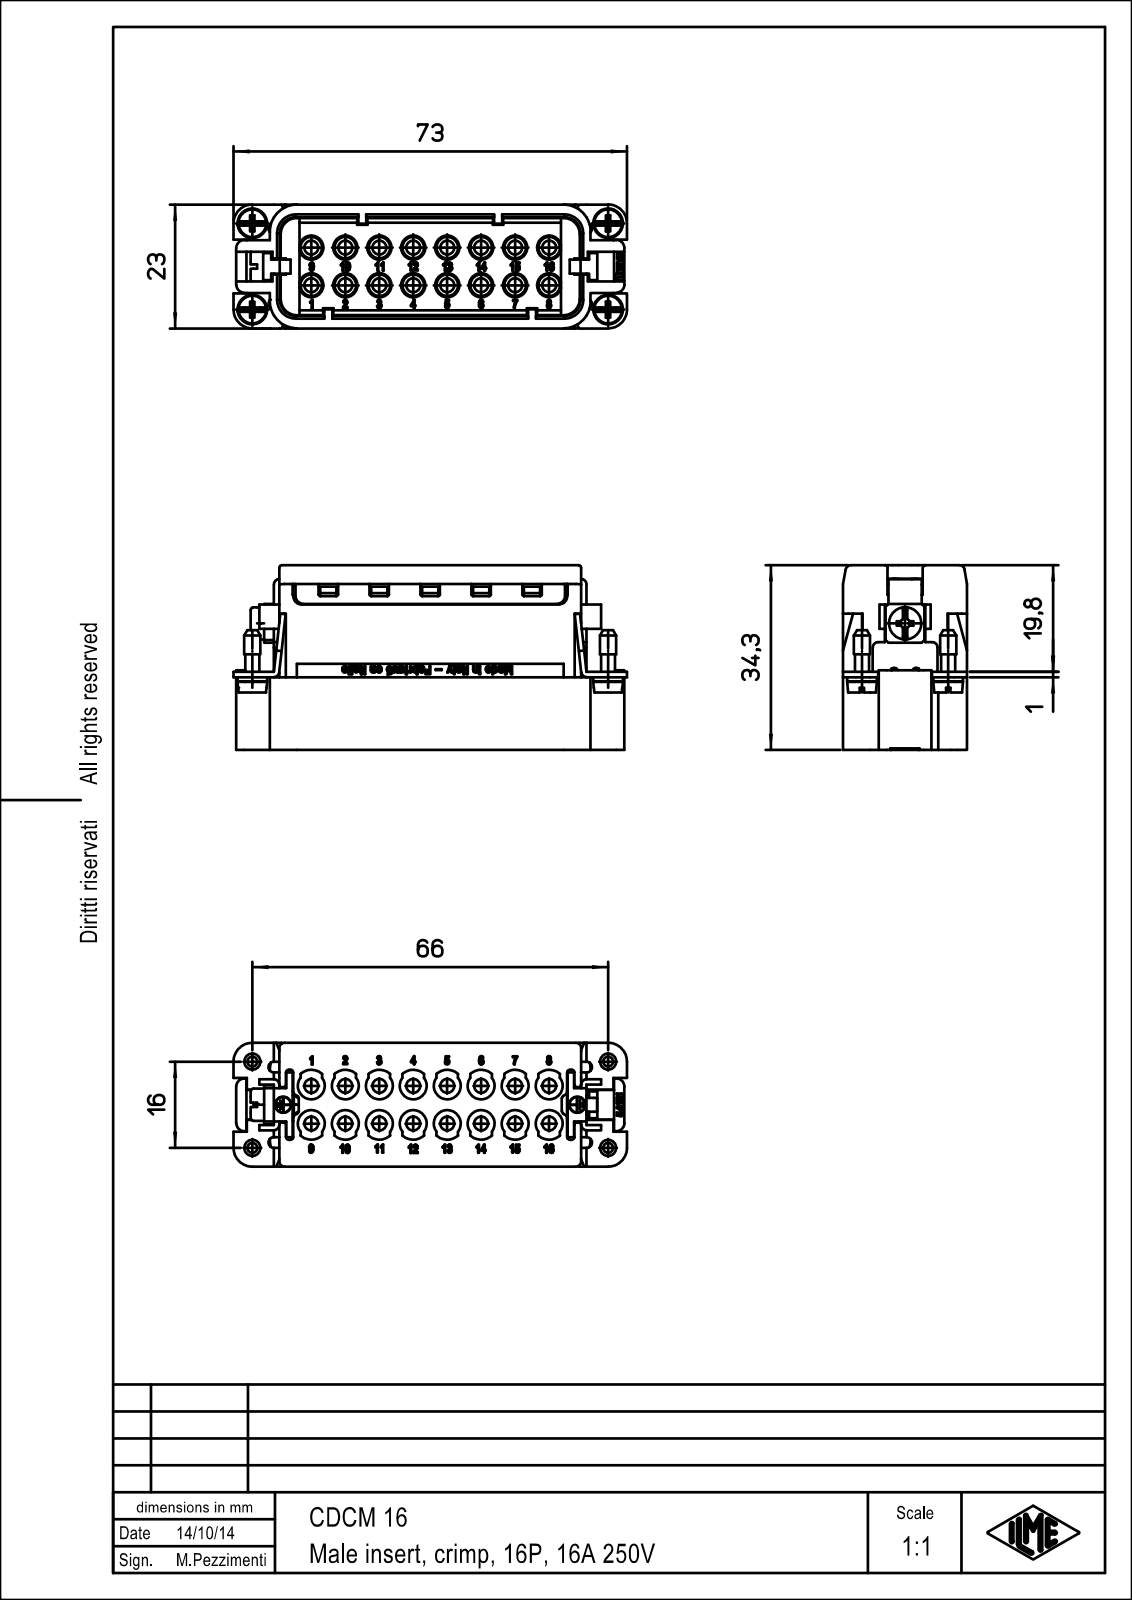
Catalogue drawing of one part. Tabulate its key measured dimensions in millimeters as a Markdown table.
| quantity | value |
| --- | --- |
| part name | CDCM_16 |
| STEP written by | PTC Creo Elements/Direct Modeling 19.0E 27-Jun-2016 (C) Parametric Technology GmbH (AUTOMOTIVE_DESIGN) |
| units | millimeters |
| bodies | 1 solid, 1579 faces (1144 planar, 301 cylindrical, 134 other) |
| overall size | 73 × 34.3 × 23 |
| volume | 41 736 mm³ |
| surface area | 18 809 mm² |
| round holes (diameter × count) | 4.6 × 16, 5 × 16, 2.6 × 15, 3 × 4, 1.8 × 1 |
| round bosses / shafts (diameter × count) | 5.5 × 4, 2.6 × 4, 6 × 1, 4.5 × 1, 3.5 × 1 |
| partial cylindrical surfaces (radius × count) | 1 × 19, 0.5 × 18, 0.3 × 12, 1.5 × 4, 3.5 × 4, 5 × 4, 0.15 × 2, 0.75 × 2 |
| main face-to-face distances | 23, 18.8, 15.5, 1, 13, 21.3, 34.3, 2, 2.5, 5.8 |
| hole center spacings | 6.3, 9.42, 12.6, 14.41, 18.9, 20.15, 7, 25.2 |
